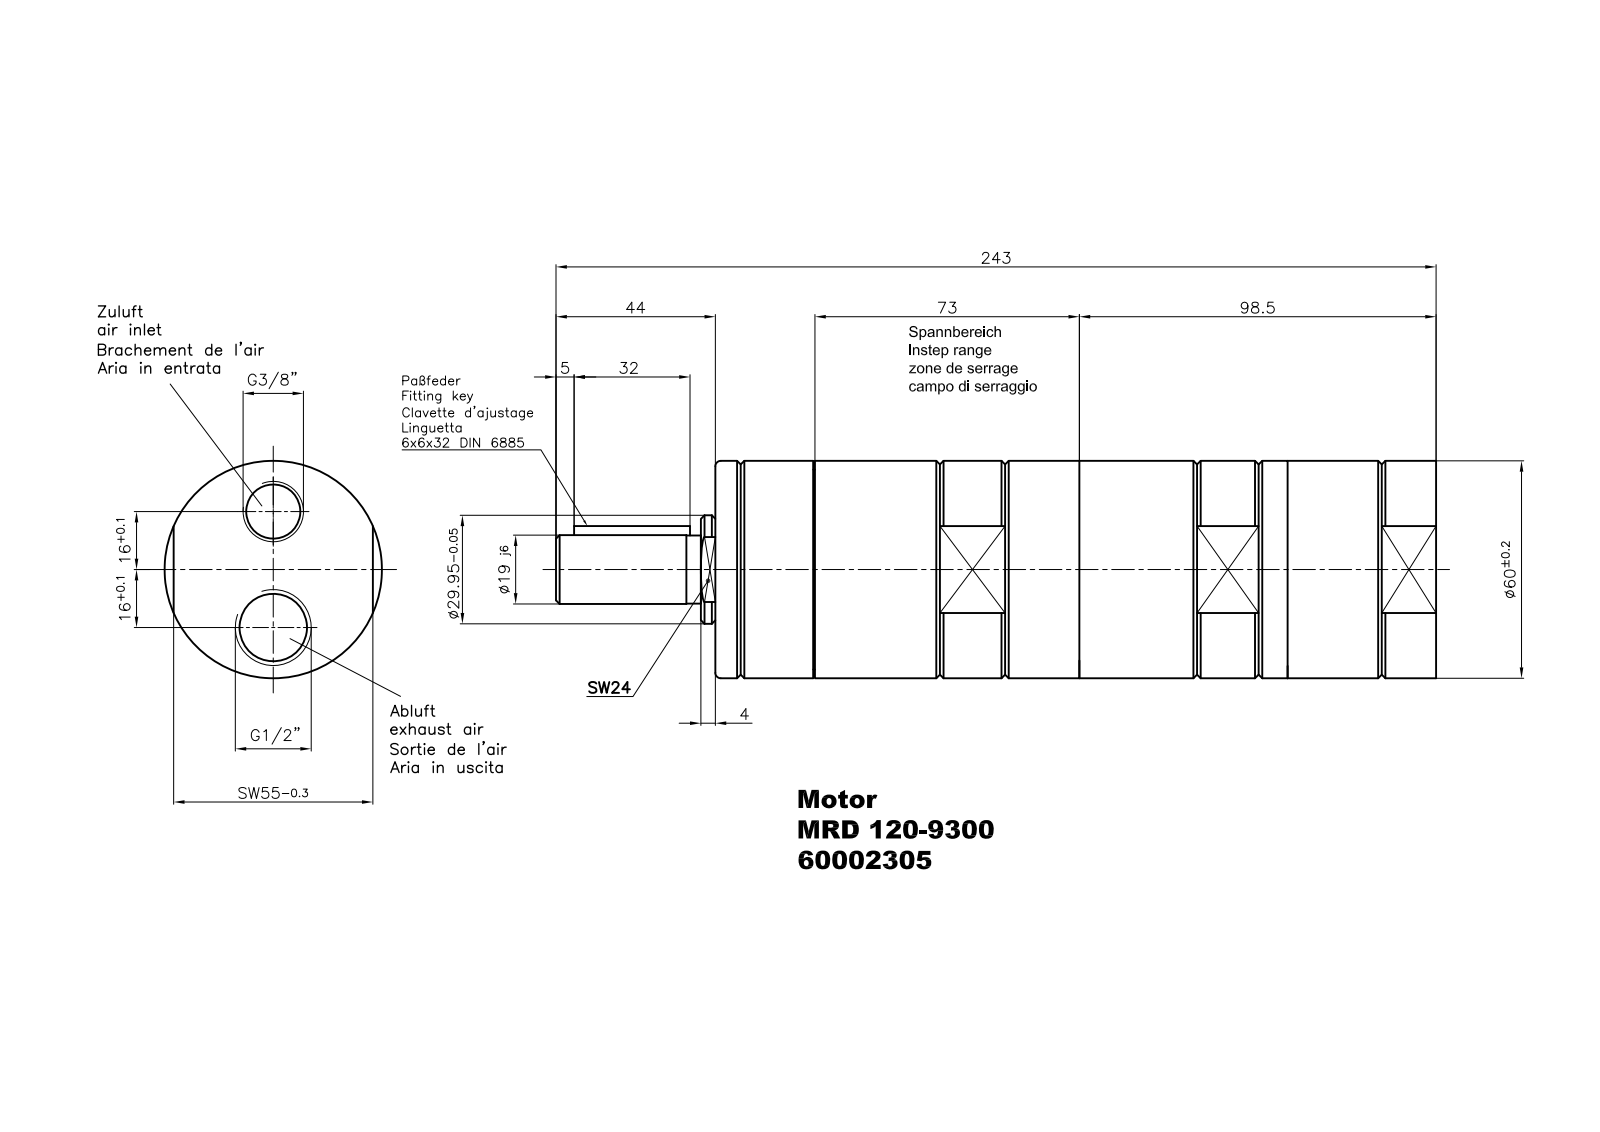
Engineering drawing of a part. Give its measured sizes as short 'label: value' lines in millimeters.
name: MRD 120-9300_60002305
written by: Autodesk Inventor 2008 (AUTOMOTIVE_DESIGN)
unit: mm
bodies: 1 solid, 127 faces (48 planar, 37 cylindrical, 42 other)
size: 243 × 60 × 60
volume: 555 238 mm³; area: 52 709 mm²
holes: 1× ⌀1.55, 1× ⌀4, 1× ⌀5.5, 1× ⌀35
bosses: 1× ⌀60, 1× ⌀58.15, 1× ⌀56.44, 1× ⌀29.95, 1× ⌀19, 1× ⌀18.8, 1× ⌀5, 1× ⌀3.6
rounds: 2× R3, 2× R7.5, 1× R8.5, 1× R23.5, 1× R26.68
face distances: 199, 55, 177.5, 21.5, 186, 8.5, 13, 100.5, 77, 85.5
